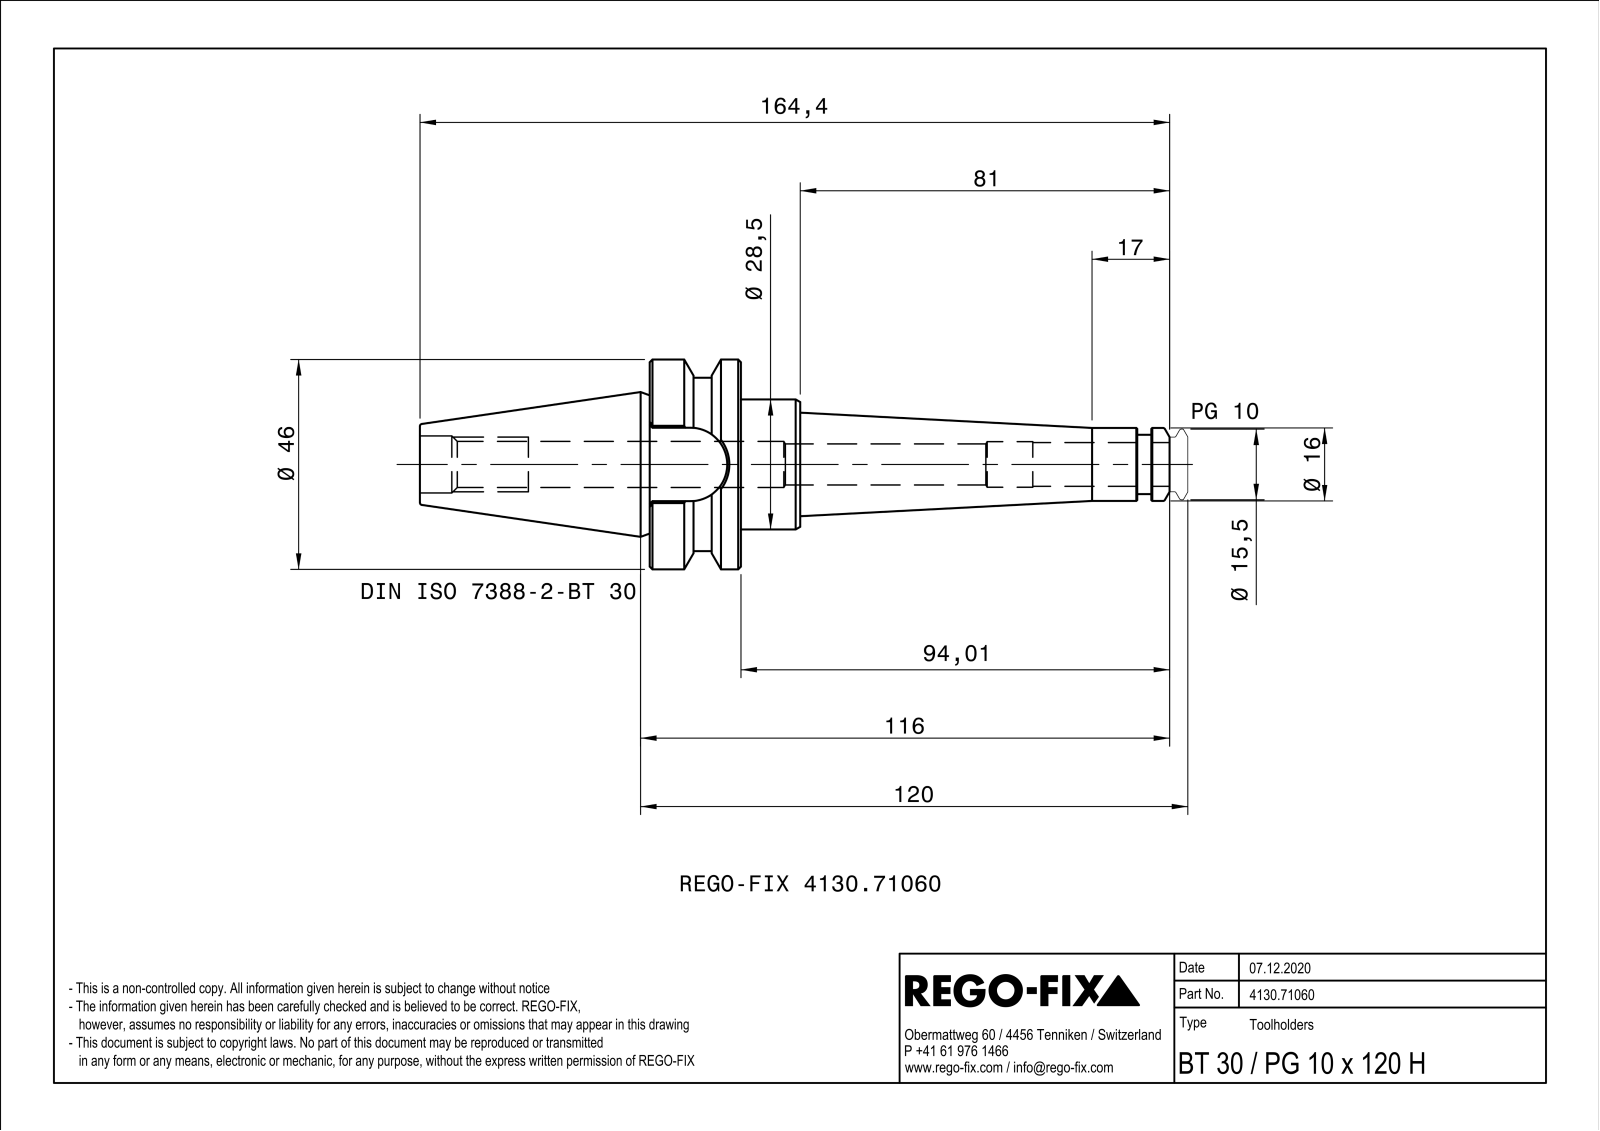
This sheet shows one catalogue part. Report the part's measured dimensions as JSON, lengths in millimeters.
{"part_name": "NOCUT", "step_written_by": "SIEMENS PLM Software Solid Edge ST10 (AUTOMOTIVE_DESIGN)", "units": "millimeters", "bodies": {"solids": 1, "faces": 108, "planar": 35, "cylindrical": 26, "other": 47}, "overall_size": [164.4, 46, 46], "volume_mm3": 70785, "surface_area_mm2": 20665, "round_holes": [[9, 1], [10, 1], [10.11, 1], [12.5, 1]], "round_bosses_or_shafts": [[46, 1], [28.5, 1], [16, 1], [13, 1]], "partial_cylinders_radius": [[0.5, 8], [8.05, 1], [19, 1]], "face_to_face_distances": [20, 32.5, 70.4, 16.1, 50.4, 3.1, 90, 110, 160.4, 86.9]}
